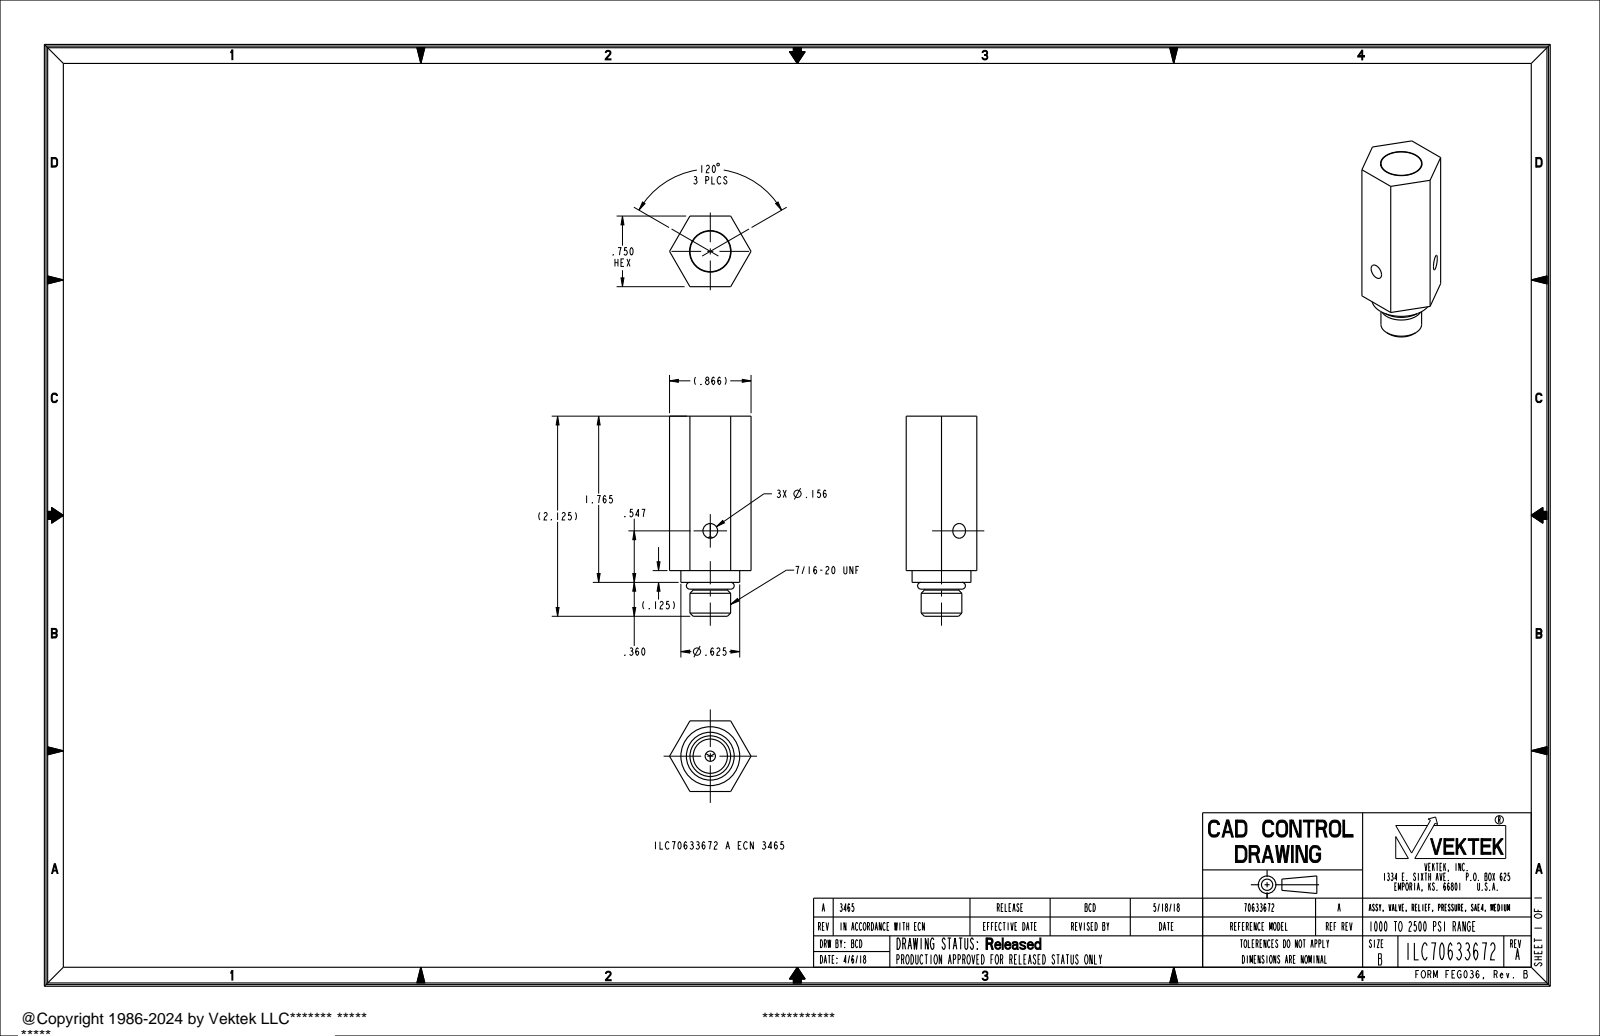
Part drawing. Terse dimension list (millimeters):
name: ILC70633672
written by: PRO/ENGINEER BY PARAMETRIC TECHNOLOGY CORPORATION, 2013320 (AUTOMOTIVE_DESIGN)
unit: mm
bodies: 2 solids, 38 faces (12 planar, 18 cylindrical, 8 other)
size: 54 × 22 × 19.1
volume: 14 100 mm³; area: 4 645 mm²
holes: 3× ⌀4, 1× ⌀2.8, 1× ⌀11.2
bosses: 1× ⌀15.9, 1× ⌀11, 1× ⌀10.9, 1× ⌀9.2
face distances: 19.1, 44.8, 3.2, 41.7, 9.1, 12.3, 54, 52.2, 43.1, 39.9
